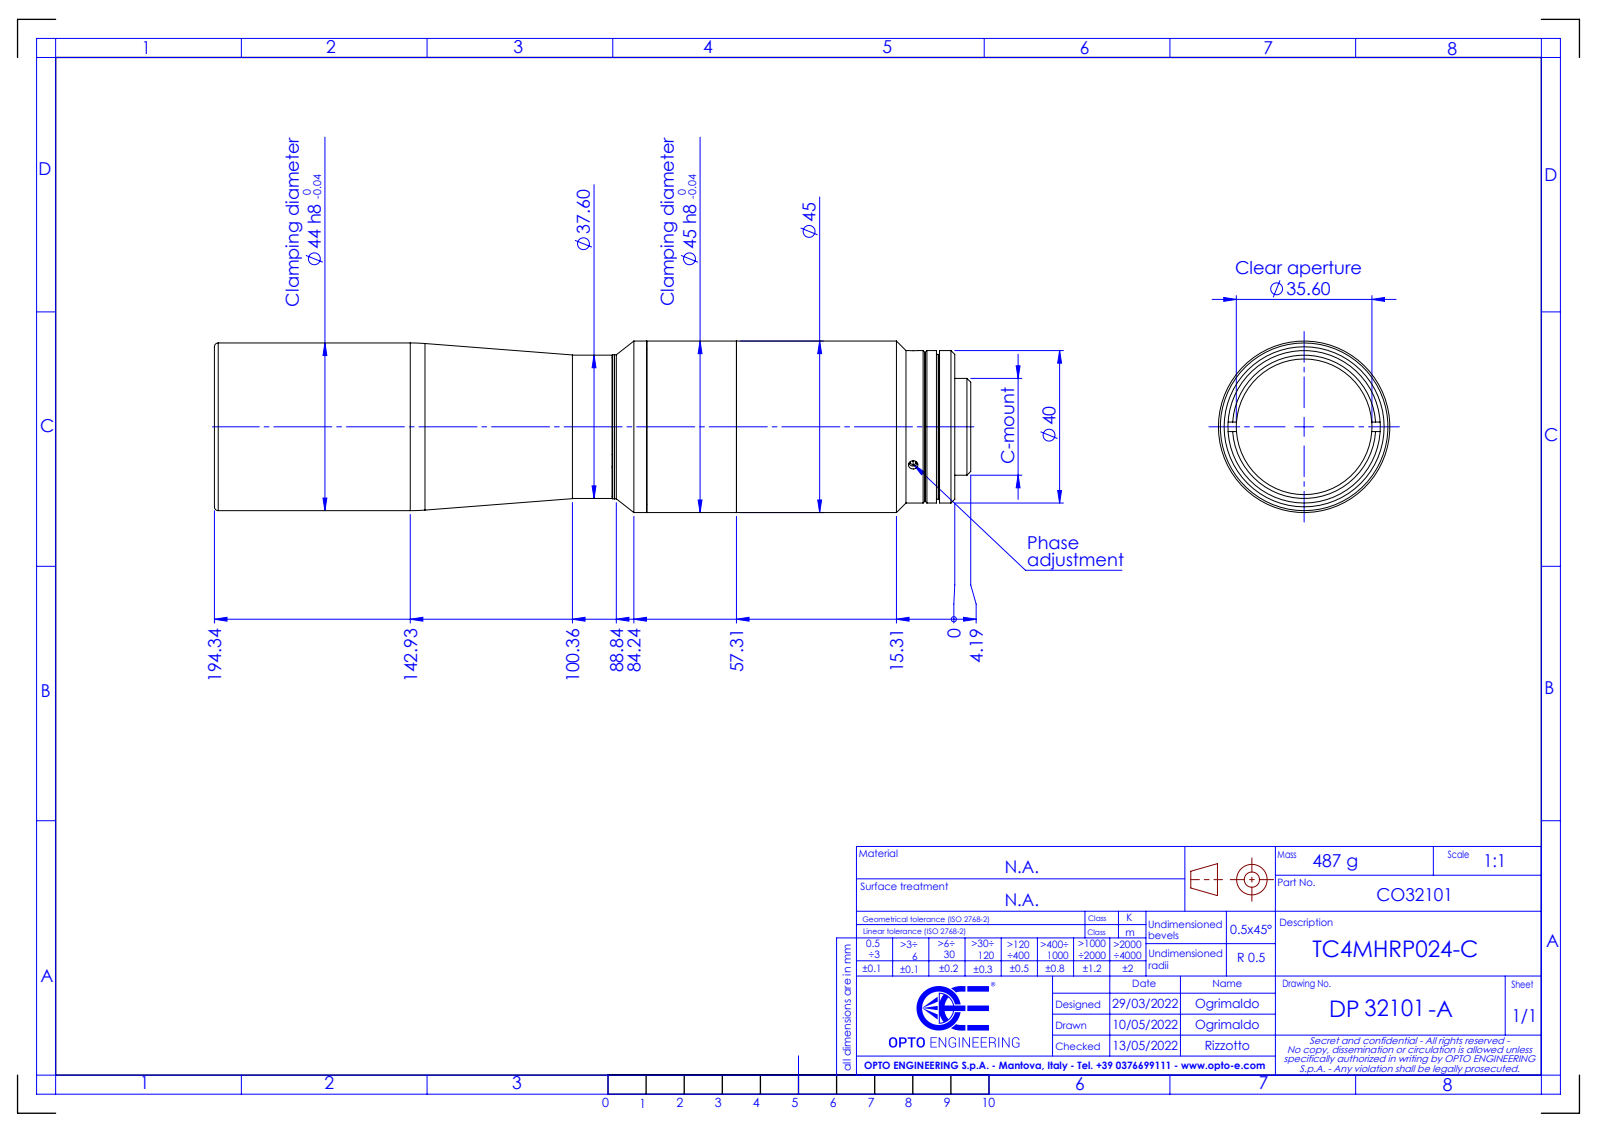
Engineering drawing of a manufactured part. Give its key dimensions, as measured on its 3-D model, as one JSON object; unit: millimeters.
{"part_name": "DP32101-A_TC4MHRP024-C", "step_written_by": "SolidWorks 2021 (CONFIG_CONTROL_DESIGN)", "units": "millimeters", "bodies": {"solids": 0, "faces": 93, "planar": 33, "cylindrical": 38, "other": 22}, "overall_size": [198.53, 45, 45], "round_holes": [[2.5, 3], [22.5, 1], [35.6, 1]], "round_bosses_or_shafts": [[45, 1], [44, 1], [40, 1], [38, 1], [37.8, 1], [37.6, 1], [25.4, 1]], "face_to_face_distances": [3.8, 3, 0.8, 7.8, 4.8, 4, 85.04, 9, 82.04, 85.84]}
